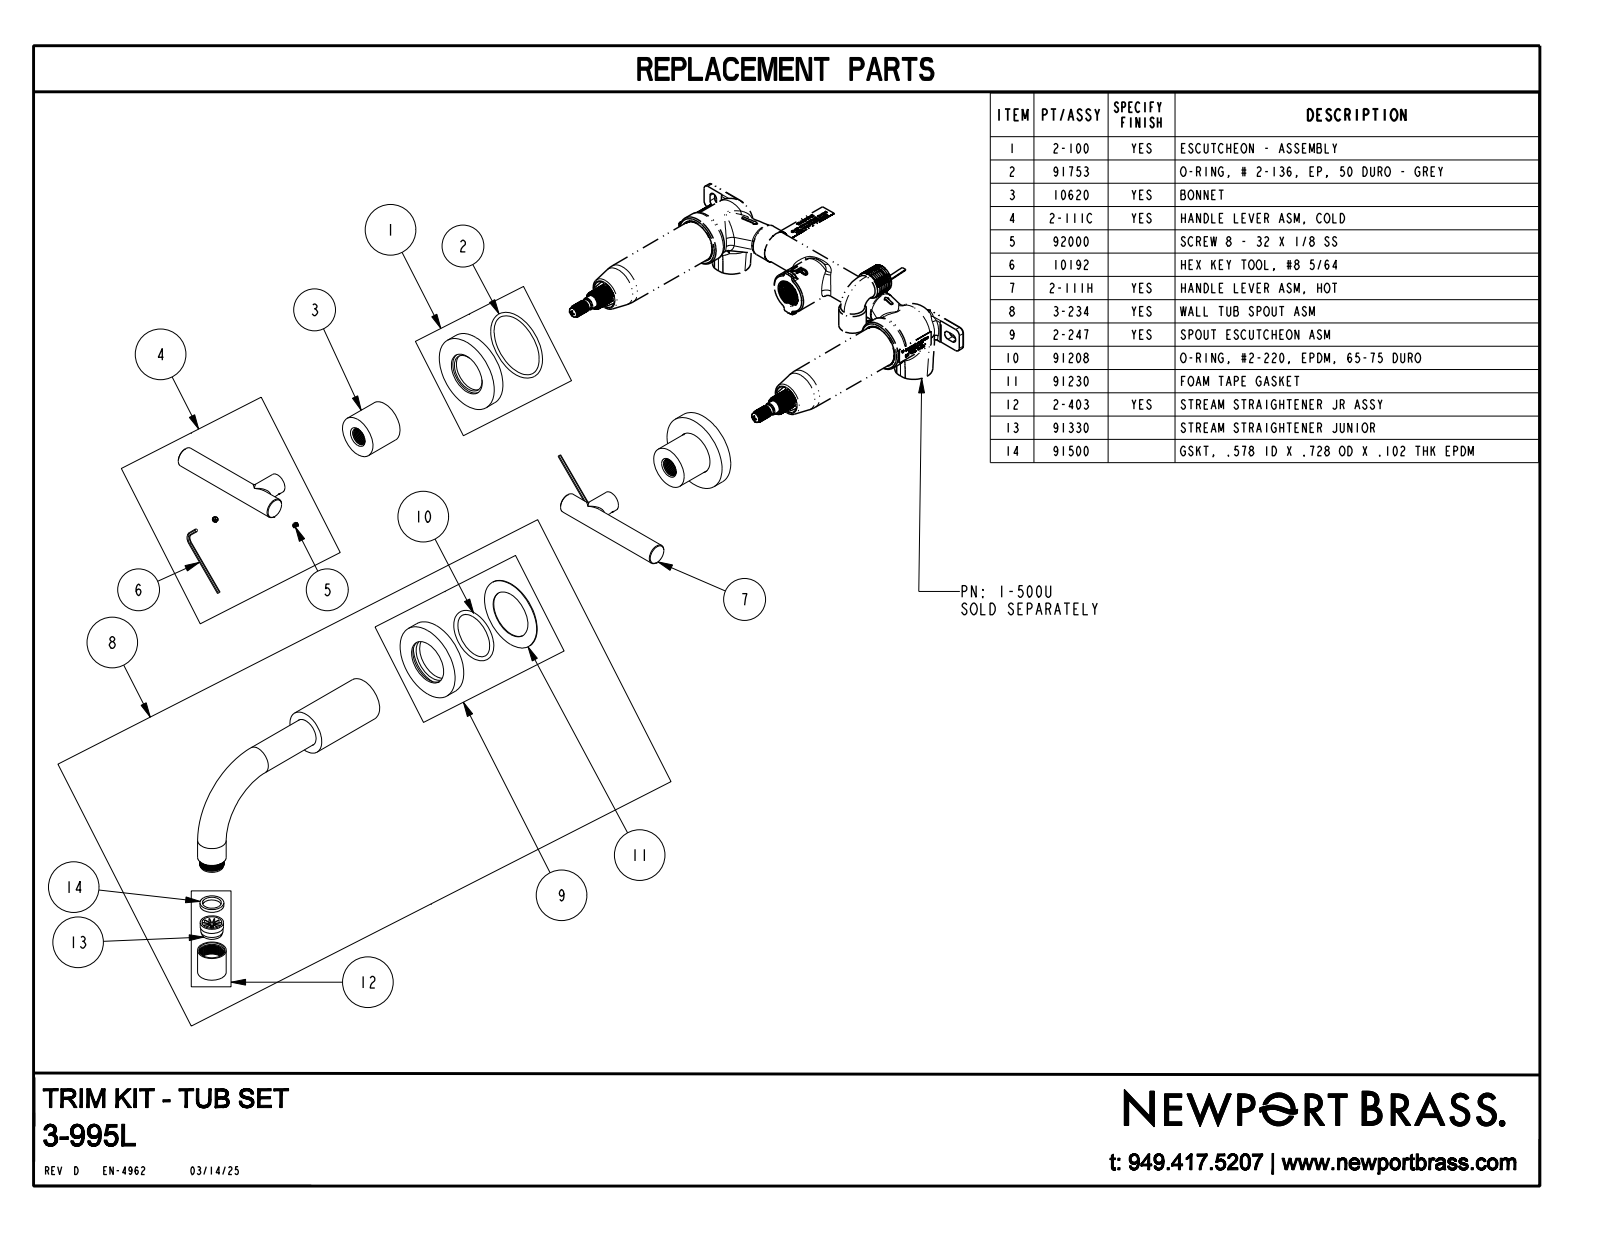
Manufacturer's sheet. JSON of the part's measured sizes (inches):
{"part_name": "3-995L_SW0001", "step_written_by": "CREO PARAMETRIC BY PTC INC, 2018400 (AUTOMOTIVE_DESIGN)", "units": "inches", "bodies": {"solids": 3, "faces": 64, "planar": 16, "cylindrical": 30, "other": 18}, "overall_size": [13.853, 10.627, 5.998], "volume_in3": 16.49, "surface_area_in2": 85.82, "round_bosses_or_shafts": [[2.375, 3], [0.625, 3], [1.313, 2], [0.875, 2], [0.5, 2], [1.375, 1]], "face_to_face_distances": [0.375, 1.483, 1.108, 1.5, 1.125, 0.017, 9.978, 3.875, 13.853, 6.103]}
